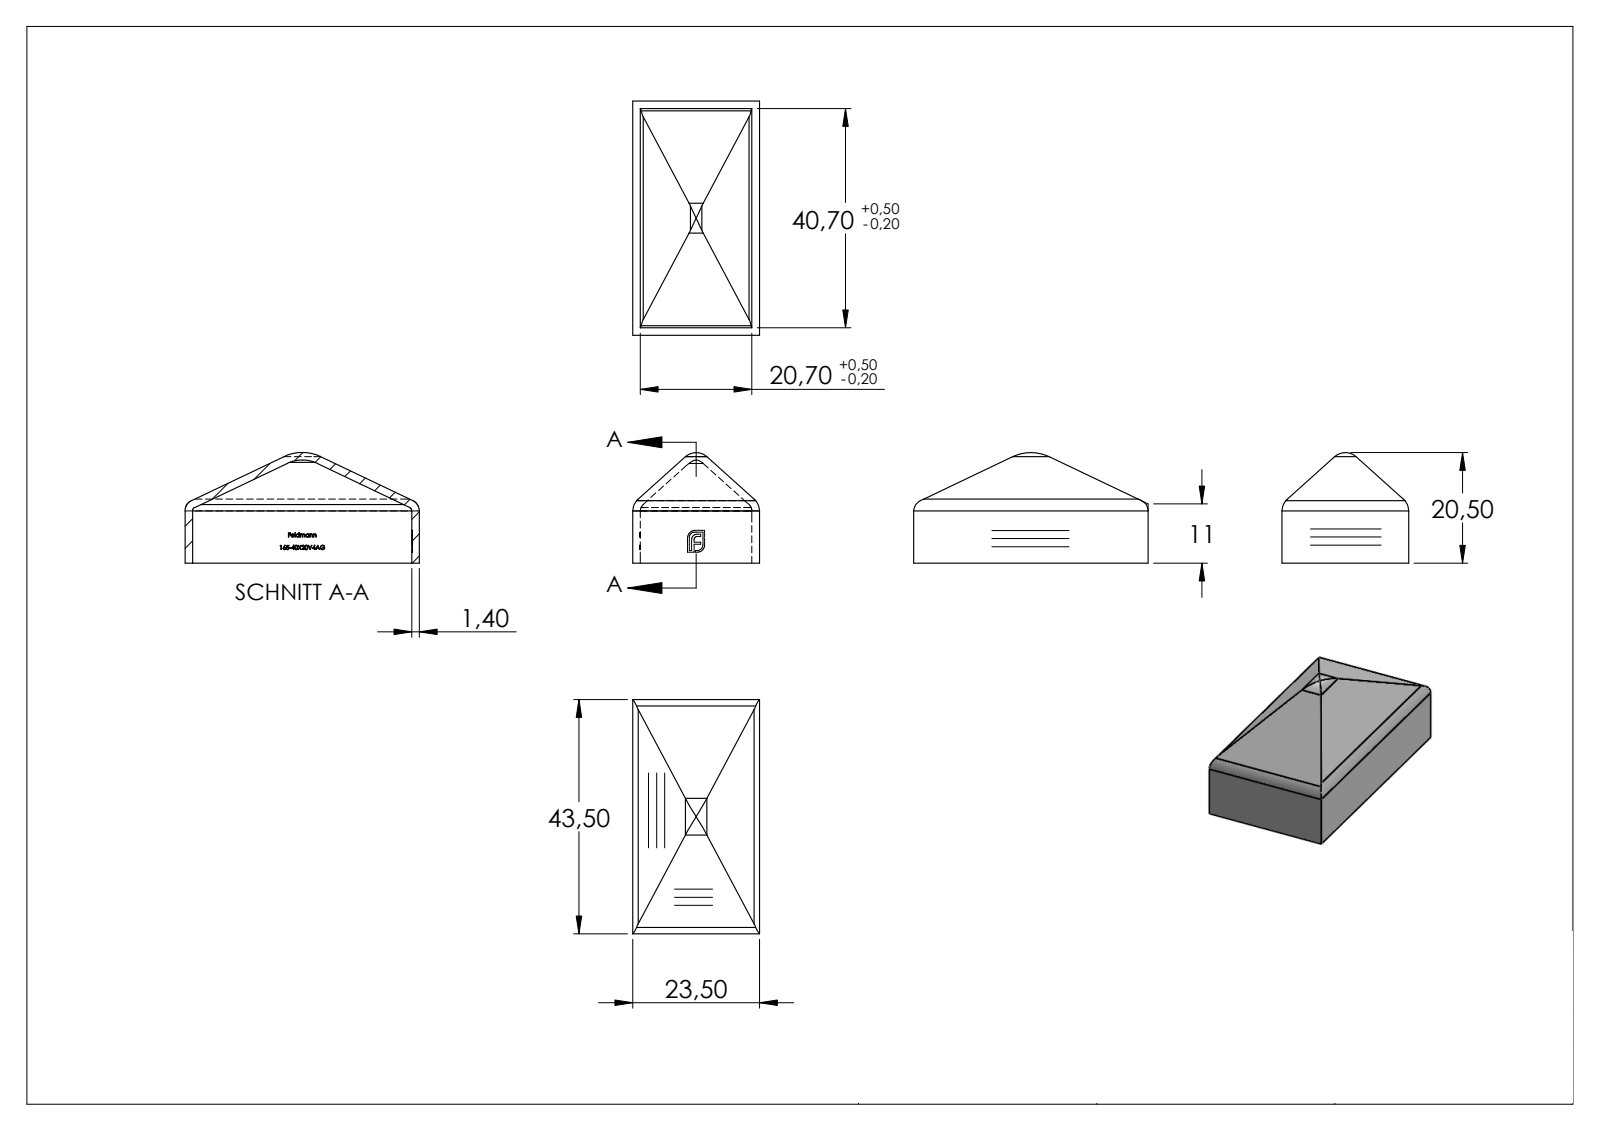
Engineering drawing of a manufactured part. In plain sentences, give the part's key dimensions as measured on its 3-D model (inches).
The part is named "165-40X20V4AG". Its 3-D file was written by "SolidWorks 2018 (CONFIG_CONTROL_DESIGN)". It is 1 solid with 341 faces: 207 planar, 16 cylindrical and 118 other. Overall it measures 1.713 by 0.925 by 0.807 inches. Its volume is 0.212 cubic inches and its surface area 8.004 square inches. Partial cylindrical surfaces (rounded edges, fillets, slot ends): 3 of radius 0.063, 3 of radius 0.118, 2 of radius 0.028, 2 of radius 0.083, 1 of radius 0.256, 1 of radius 0.311. The main face-to-face distances are 0.055, 0.87, 0.925, 1.657, 0.815, 1.713, 1.602, 0.051, 1.606, 1.661.
